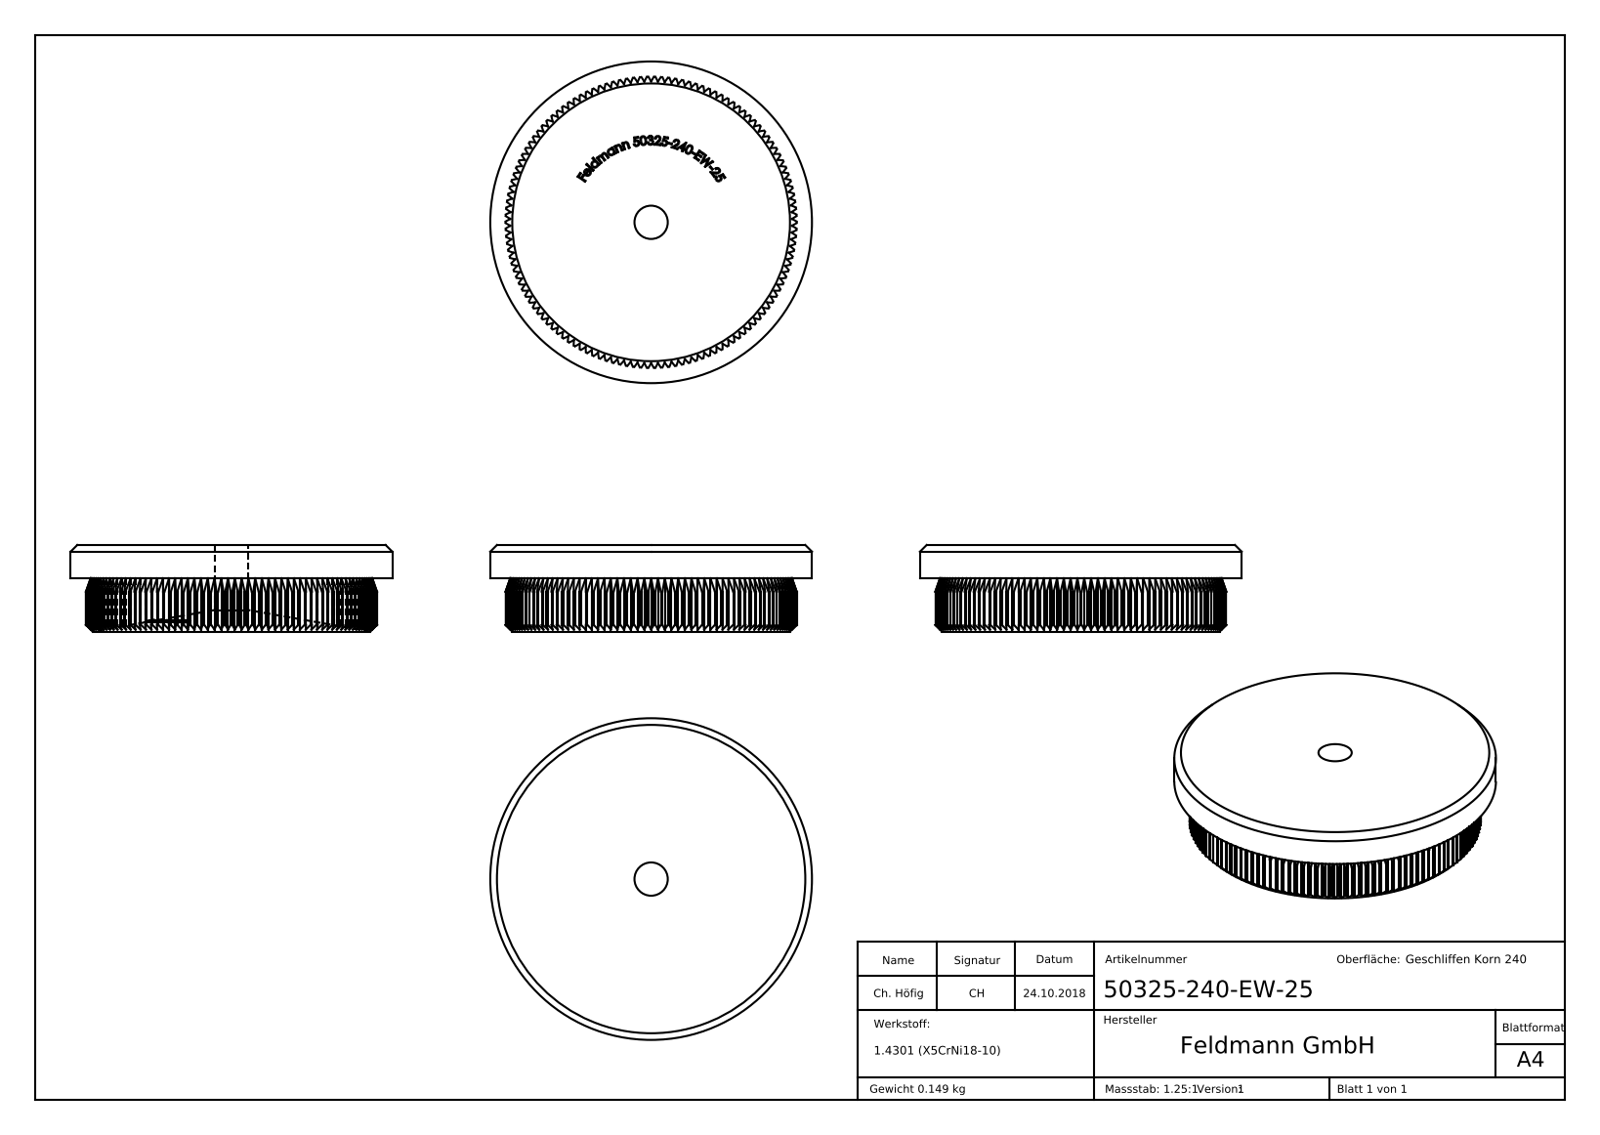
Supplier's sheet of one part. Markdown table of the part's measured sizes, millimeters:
| quantity | value |
| --- | --- |
| part name | 50325-240-EW-25 |
| STEP written by | SolidWorks 2015 (CONFIG_CONTROL_DESIGN) |
| units | millimeters |
| bodies | 1 solid, 826 faces (405 planar, 134 cylindrical, 287 other) |
| overall size | 48.3 × 48.3 × 13 |
| volume | 18 843 mm³ |
| surface area | 6 246 mm² |
| round holes (diameter × count) | 5 × 1 |
| round bosses / shafts (diameter × count) | 48.3 × 1 |
| partial cylindrical surfaces (radius × count) | 21.85 × 1 |
| main face-to-face distances | 5, 21.16, 21.14, 21.18, 21.12, 0.72, 0.53, 0.66, 1.32, 0.55 |
